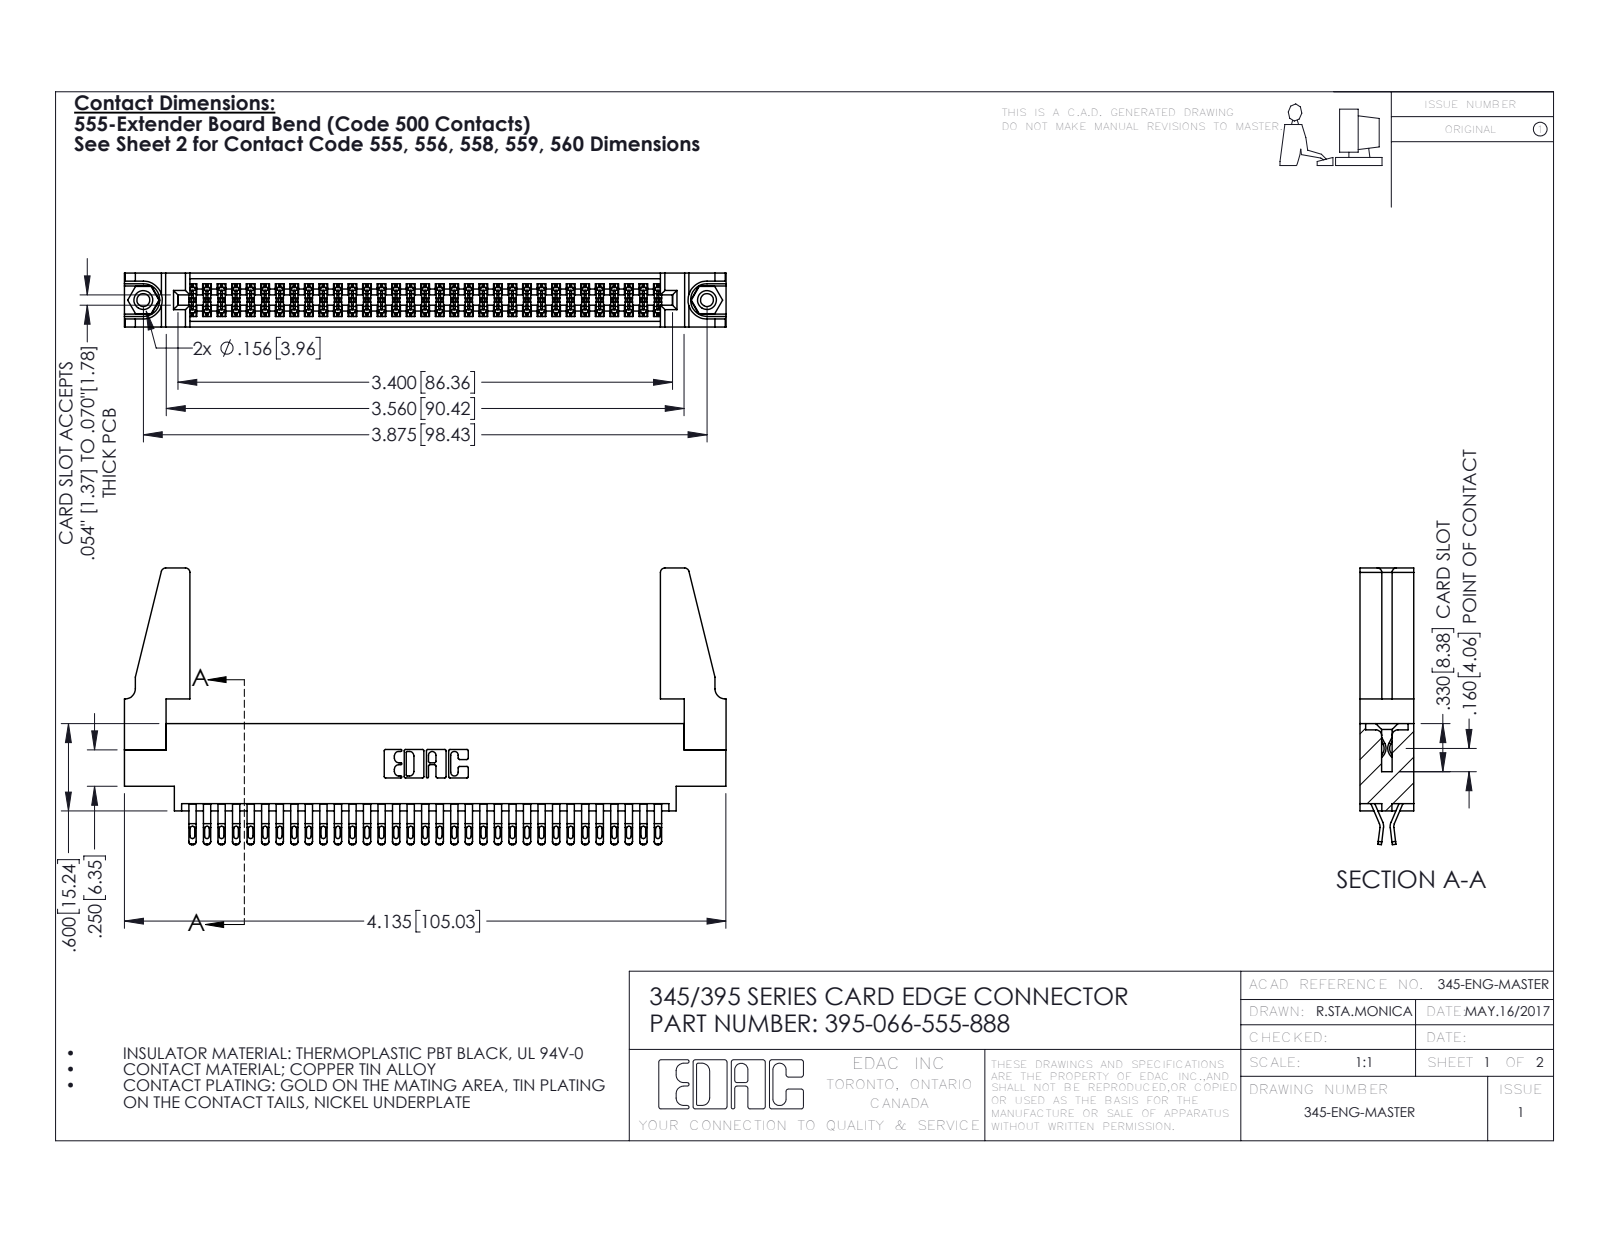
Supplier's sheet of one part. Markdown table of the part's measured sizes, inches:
| quantity | value |
| --- | --- |
| part name | 395-066-555-888; 345 Part_0.170 Offset - 0.156 Dia-TH; 345-250-001_345-250-001-102; 345-292-001_555 Tail (+1 more) |
| STEP written by | SolidWorks 2016 (CONFIG_CONTROL_DESIGN) |
| units | inches |
| bodies | 71 solids, 3950 faces (2202 planar, 1732 cylindrical, 16 other) |
| overall size | 4.136 × 1.902 × 0.37 |
| volume | 0.821 in³ |
| surface area | 29.19 in² |
| round holes (diameter × count) | 0.089 × 2, 0.125 × 2, 0.156 × 2, 0.064 × 1 |
| round bosses / shafts (diameter × count) | 0.155 × 2 |
| partial cylindrical surfaces (radius × count) | 0.016 × 165, 0.02 × 132, 0.006 × 99, 0.01 × 22, 0.03 × 8, 0.007 × 6, 0.031 × 6, 0.026 × 3 |
| main face-to-face distances | 0.072, 0.37, 0.298, 0.025, 0.2, 0.098, 0.272, 0.225, 0.175, 0.149 |
| hole center spacings | 0.27, 3.64, 3.875 |
